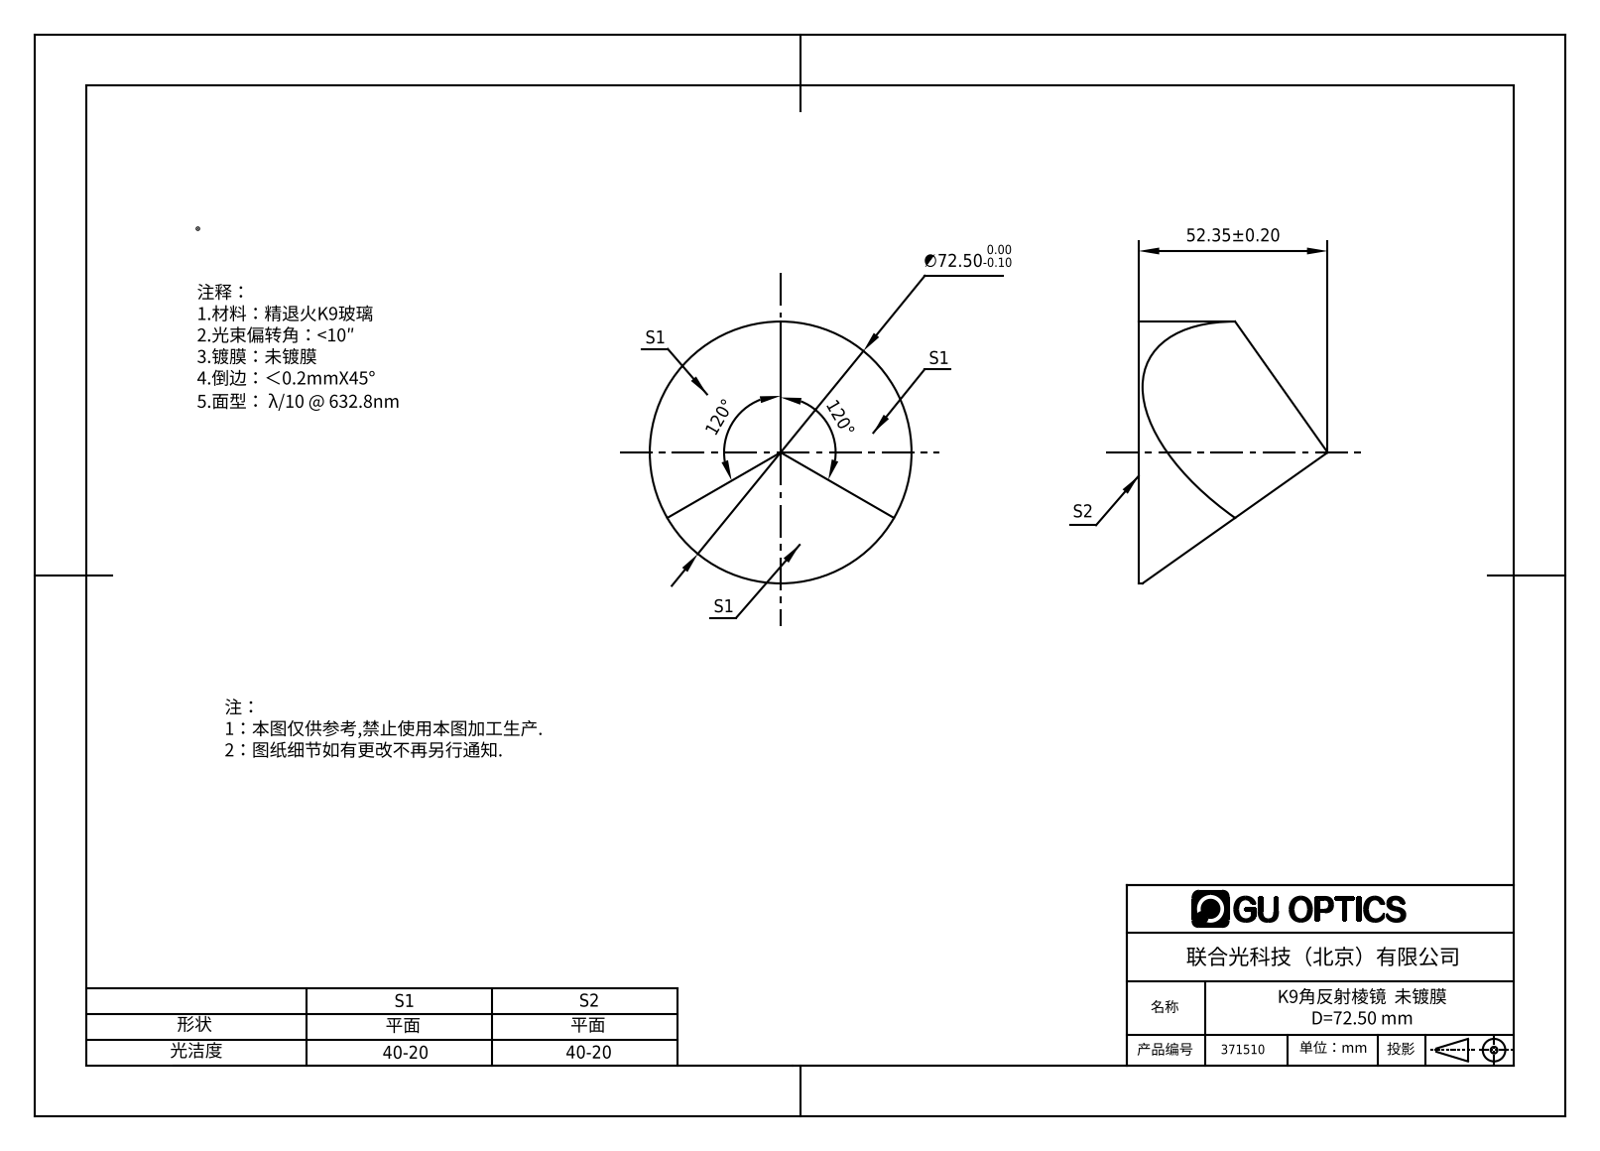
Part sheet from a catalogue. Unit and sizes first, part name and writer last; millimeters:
Units: millimetres
Overall size (bounding box): 72.5 × 72.5 × 52.35
Round bosses / shafts (diameter × count): ⌀72.5 ×1
Volume: 99 457 mm³ · Surface area: 13 547 mm²
Bodies: 1 solid, 6 faces (4 planar, 2 cylindrical, 0 other)
Part name (STEP PRODUCT): 371510
STEP written by: SolidWorks 2016 (CONFIG_CONTROL_DESIGN)
